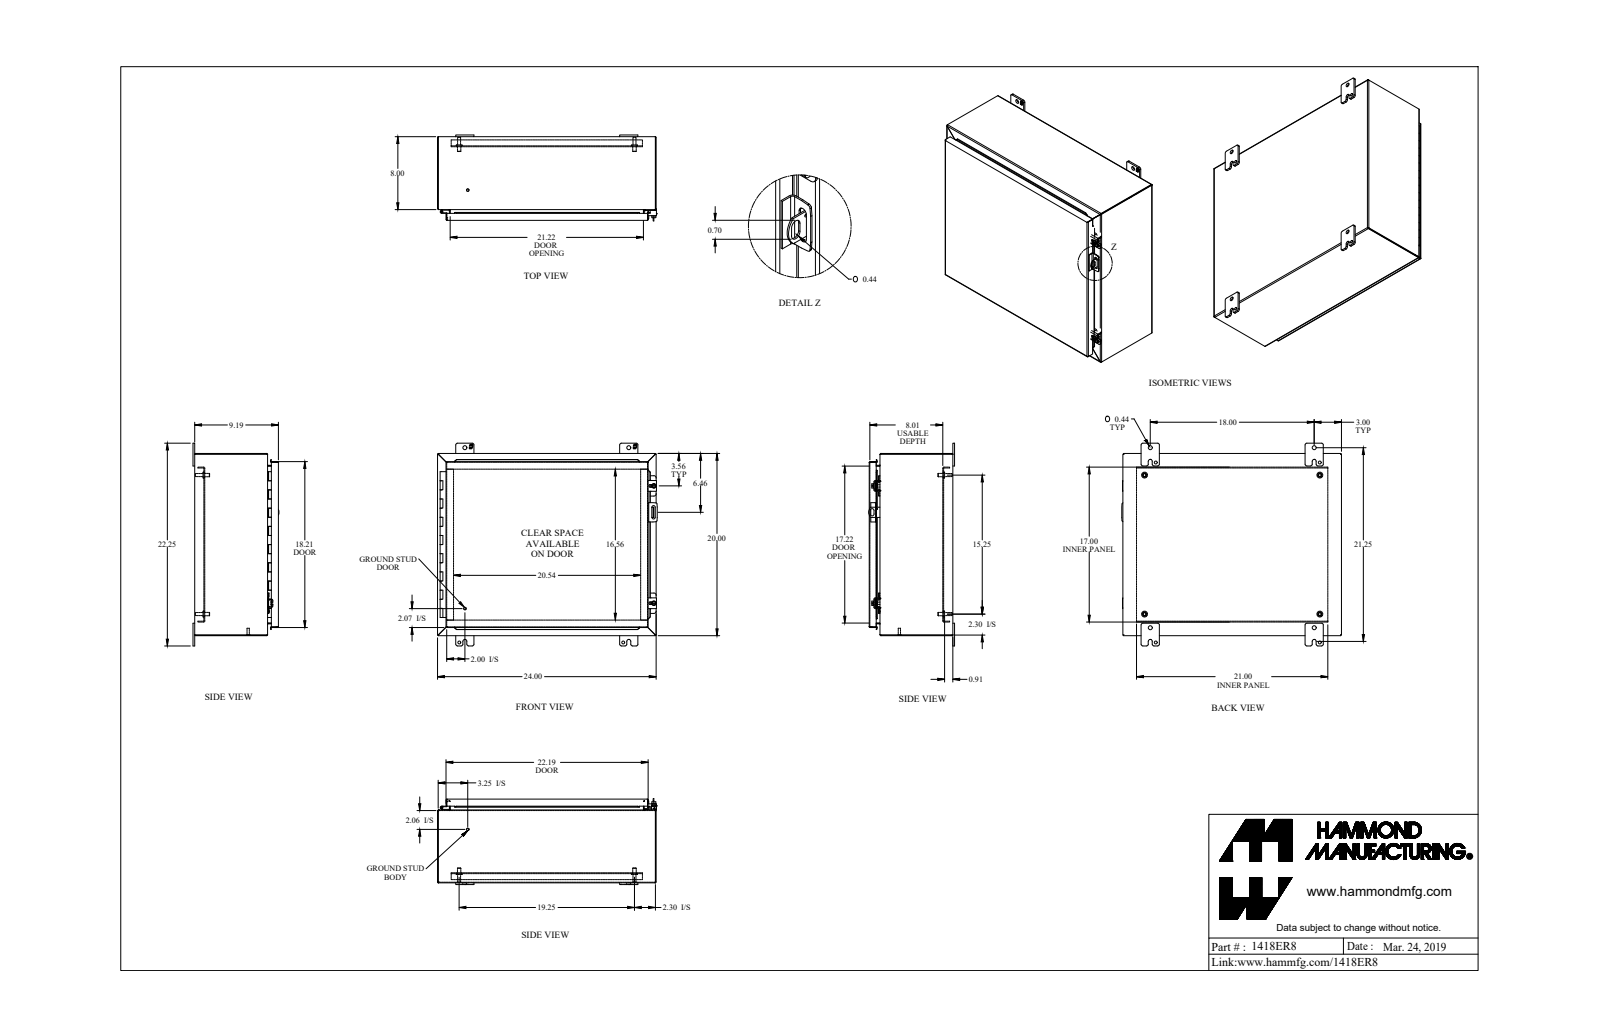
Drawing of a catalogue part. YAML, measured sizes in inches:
part_name: "1418ER8"
step_written_by: "SolidWorks 2019 (AUTOMOTIVE_DESIGN)"
units: inches
bodies: {solids: 38, faces: 978, planar: 671, cylindrical: 255, other: 52}
overall_size: [24.125, 22.25, 9.437]
volume: 188.7
surface_area: 4888
round_holes:
  - {diameter: 0.313, count: 4}
  - {diameter: 0.437, count: 4}
  - {diameter: 0.5, count: 4}
  - {diameter: 0.213, count: 2}
  - {diameter: 0.265, count: 2}
  - {diameter: 0.307, count: 2}
  - {diameter: 0.375, count: 2}
  - {diameter: 0.445, count: 2}
  - {diameter: 0.125, count: 1}
  - {diameter: 0.187, count: 1}
round_bosses_or_shafts:
  - {diameter: 0.65, count: 4}
  - {diameter: 0.375, count: 4}
  - {diameter: 0.33, count: 4}
  - {diameter: 1, count: 2}
  - {diameter: 0.5, count: 2}
  - {diameter: 0.39, count: 2}
  - {diameter: 0.281, count: 2}
  - {diameter: 0.25, count: 2}
partial_cylinders:
  - {radius: 0.188, count: 26}
  - {radius: 0.036, count: 20}
  - {radius: 0.108, count: 20}
  - {radius: 0.048, count: 13}
  - {radius: 0.143, count: 13}
  - {radius: 0.007, count: 8}
  - {radius: 0.045, count: 8}
  - {radius: 0.079, count: 8}
face_to_face_distances: [0.072, 9.113, 9.041, 9.185, 0.937, 0.095, 1.009, 19.928, 8.081, 8.009]
hole_center_spacings: [18, 19.25, 24.559, 26.722, 1.736, 19.75, 21.408, 25.587]
